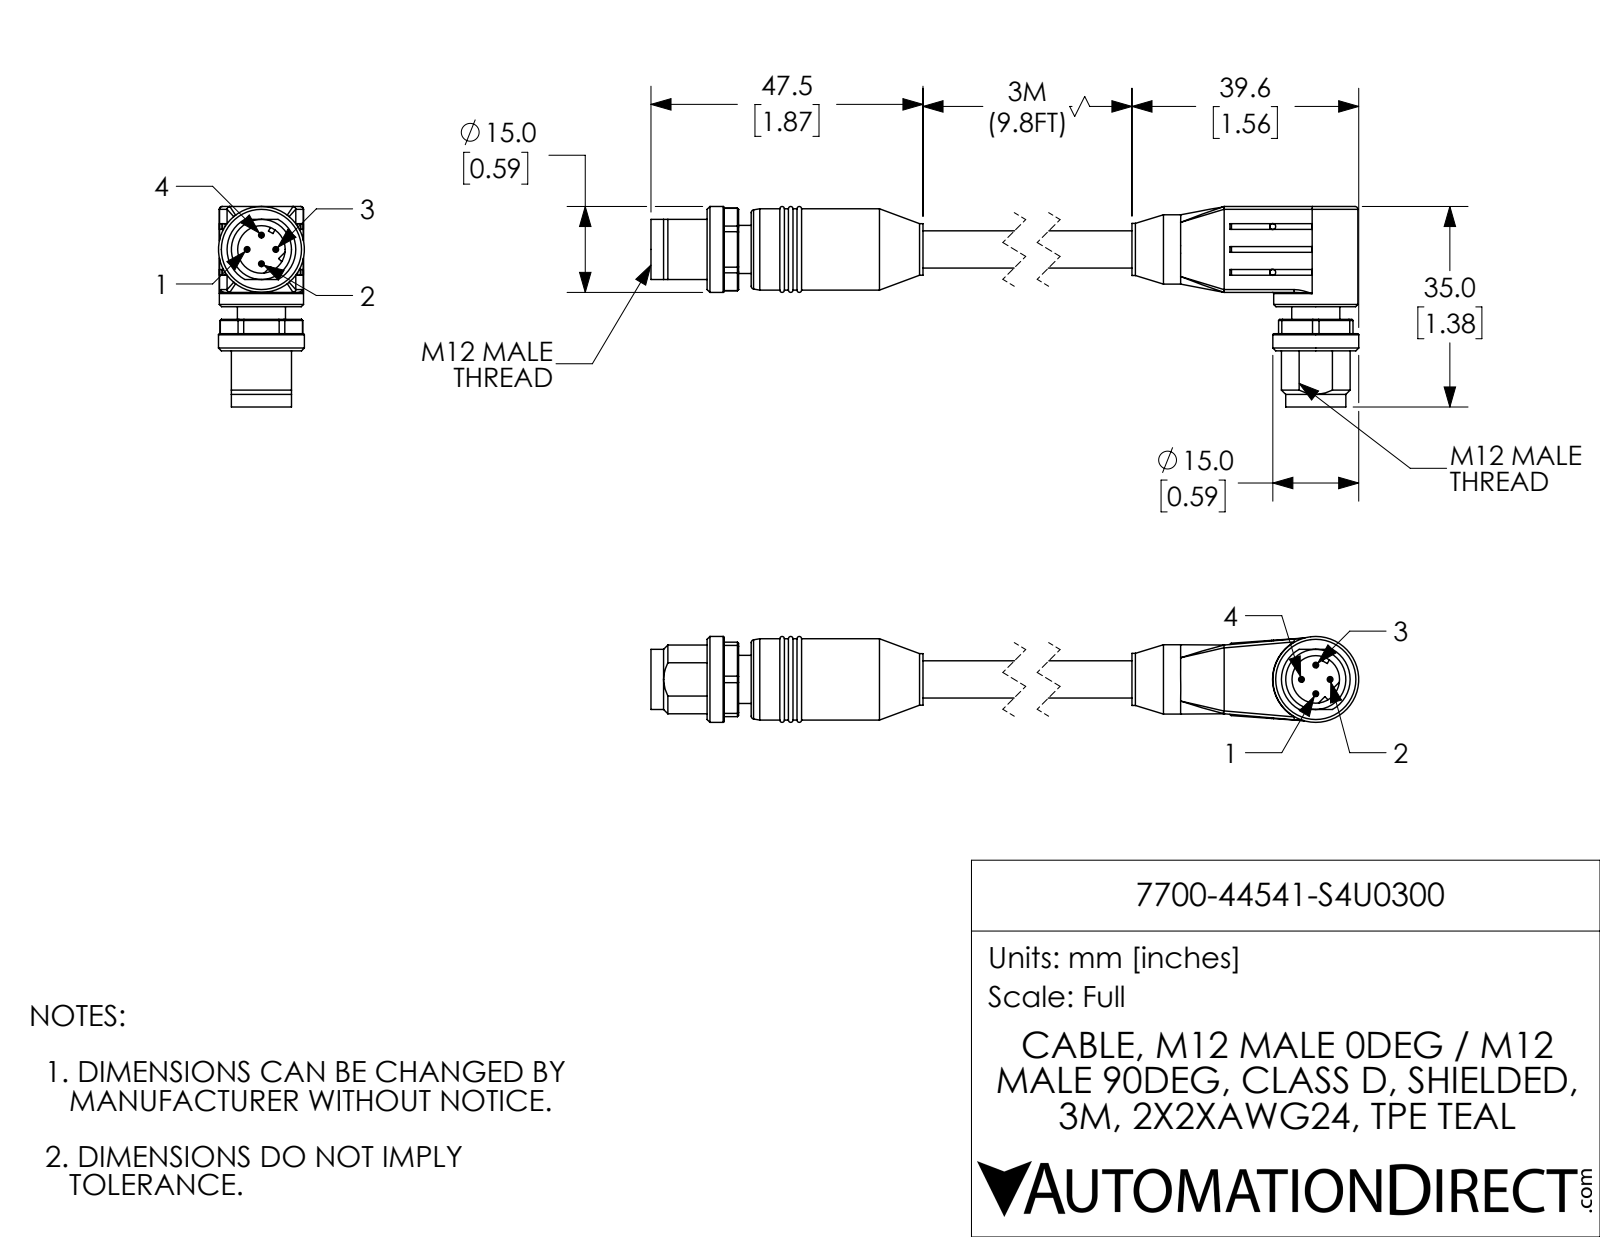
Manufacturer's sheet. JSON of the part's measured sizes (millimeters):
{"part_name": "7700-44541-S4U0300; 7700-44541-S4U0300_MALE90; 7700-44541-S4U0300_MALE", "step_written_by": "SolidWorks 2017 (AUTOMOTIVE_DESIGN)", "units": "millimeters", "bodies": {"solids": 2, "faces": 284, "planar": 114, "cylindrical": 90, "other": 80}, "overall_size": [139.1, 35, 15], "volume_mm3": 15600, "surface_area_mm2": 7045, "round_holes": [[1, 4], [8.3, 2], [4.8, 1]], "round_bosses_or_shafts": [[1, 8], [15, 2], [10.5, 2], [8.4, 2], [14.7, 1], [14.2, 1], [12.1, 1], [9.1, 1]], "partial_cylinders_radius": [[0.5, 4], [0.3, 2], [6, 2], [7.2, 2]], "face_to_face_distances": [17.5, 2.2, 2.5, 4.7, 15, 0.9, 6.4, 8.6, 5.5, 7.7], "hole_center_spacings": [8]}
